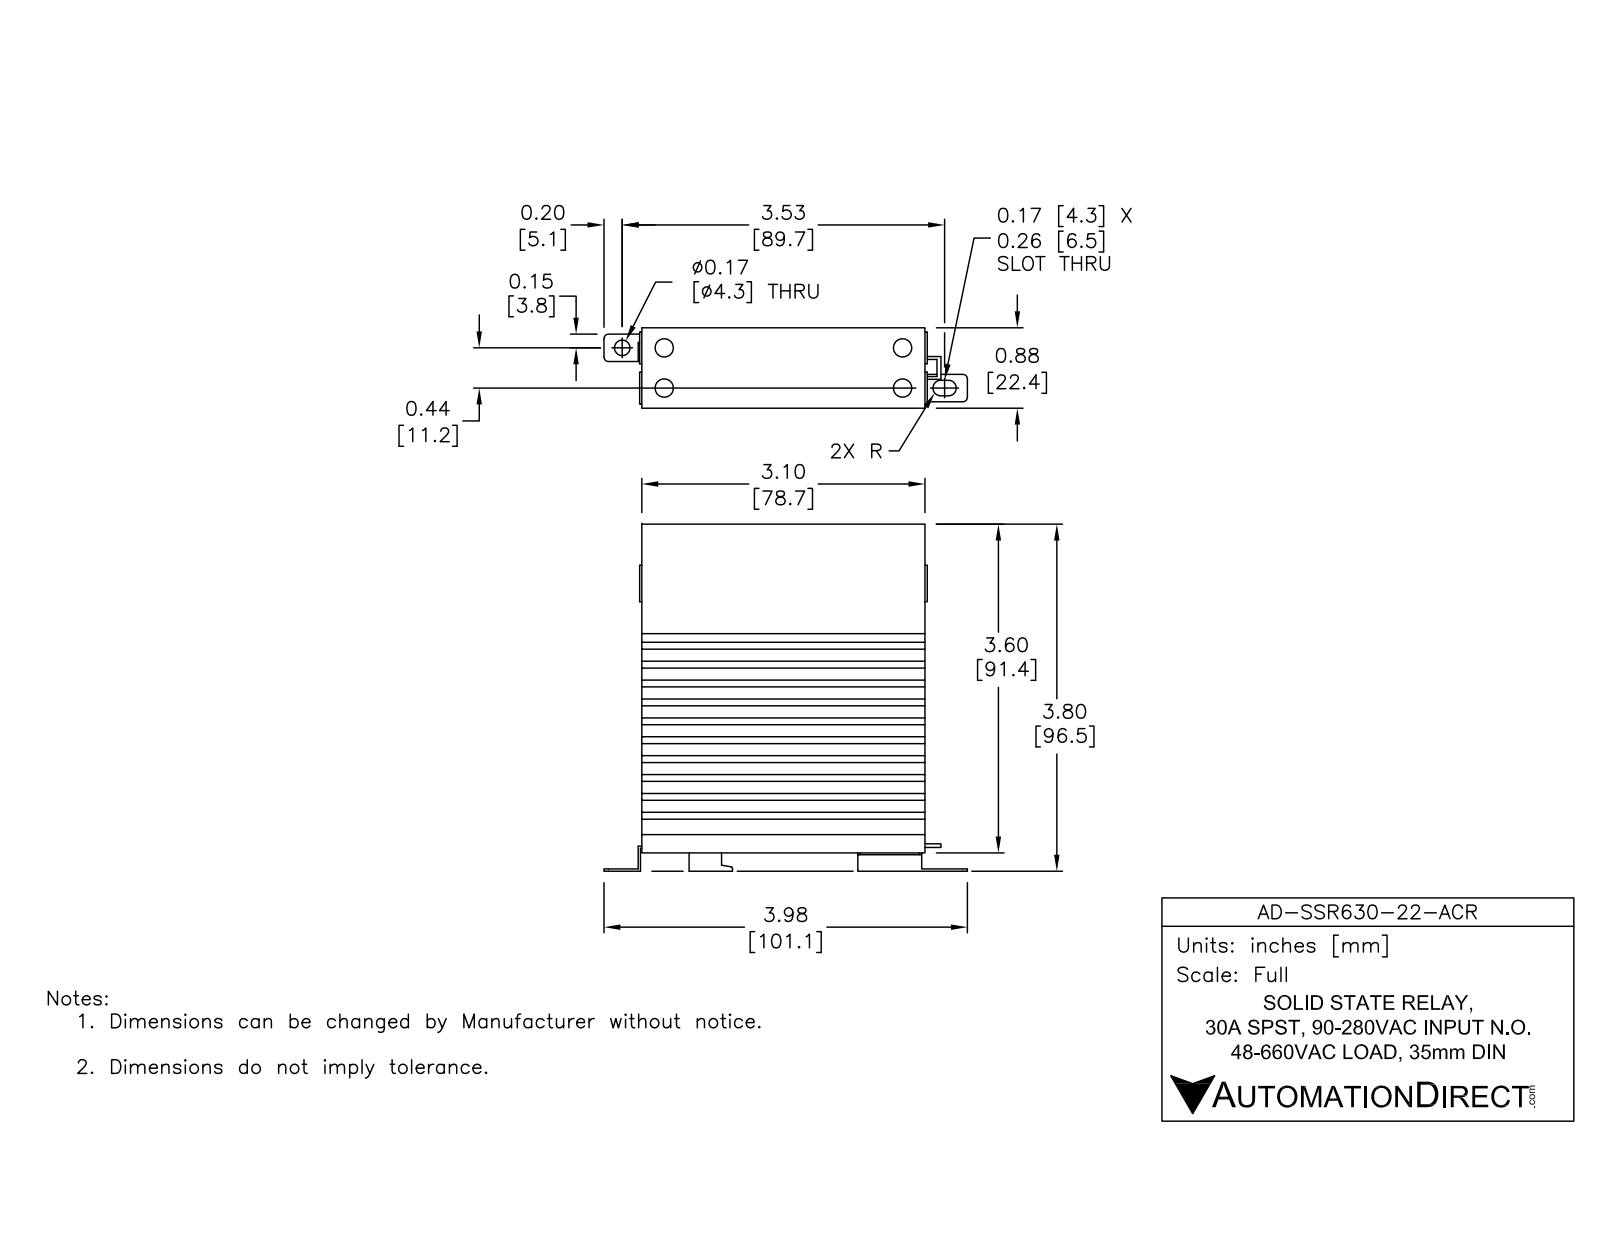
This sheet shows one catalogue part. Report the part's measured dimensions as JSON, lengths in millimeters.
{"part_name": "AD-SSR630-22-ACR", "step_written_by": "SolidWorks 2014 (AUTOMOTIVE_DESIGN)", "units": "millimeters", "bodies": {"solids": 1, "faces": 215, "planar": 195, "cylindrical": 20, "other": 0}, "overall_size": [101.1, 96.5, 22.4], "volume_mm3": 116900, "surface_area_mm2": 48330, "round_holes": [[5.1, 4], [4.3, 1]], "partial_cylinders_radius": [[1.3, 6], [2.2, 2], [0.4, 1]], "face_to_face_distances": [15.7, 5.3, 21, 10.5, 3.4, 12.4, 8.6, 10.5, 1.9, 5.3], "hole_center_spacings": [11.2, 66.3, 67.2, 11.7, 16.2, 78, 78.8]}
